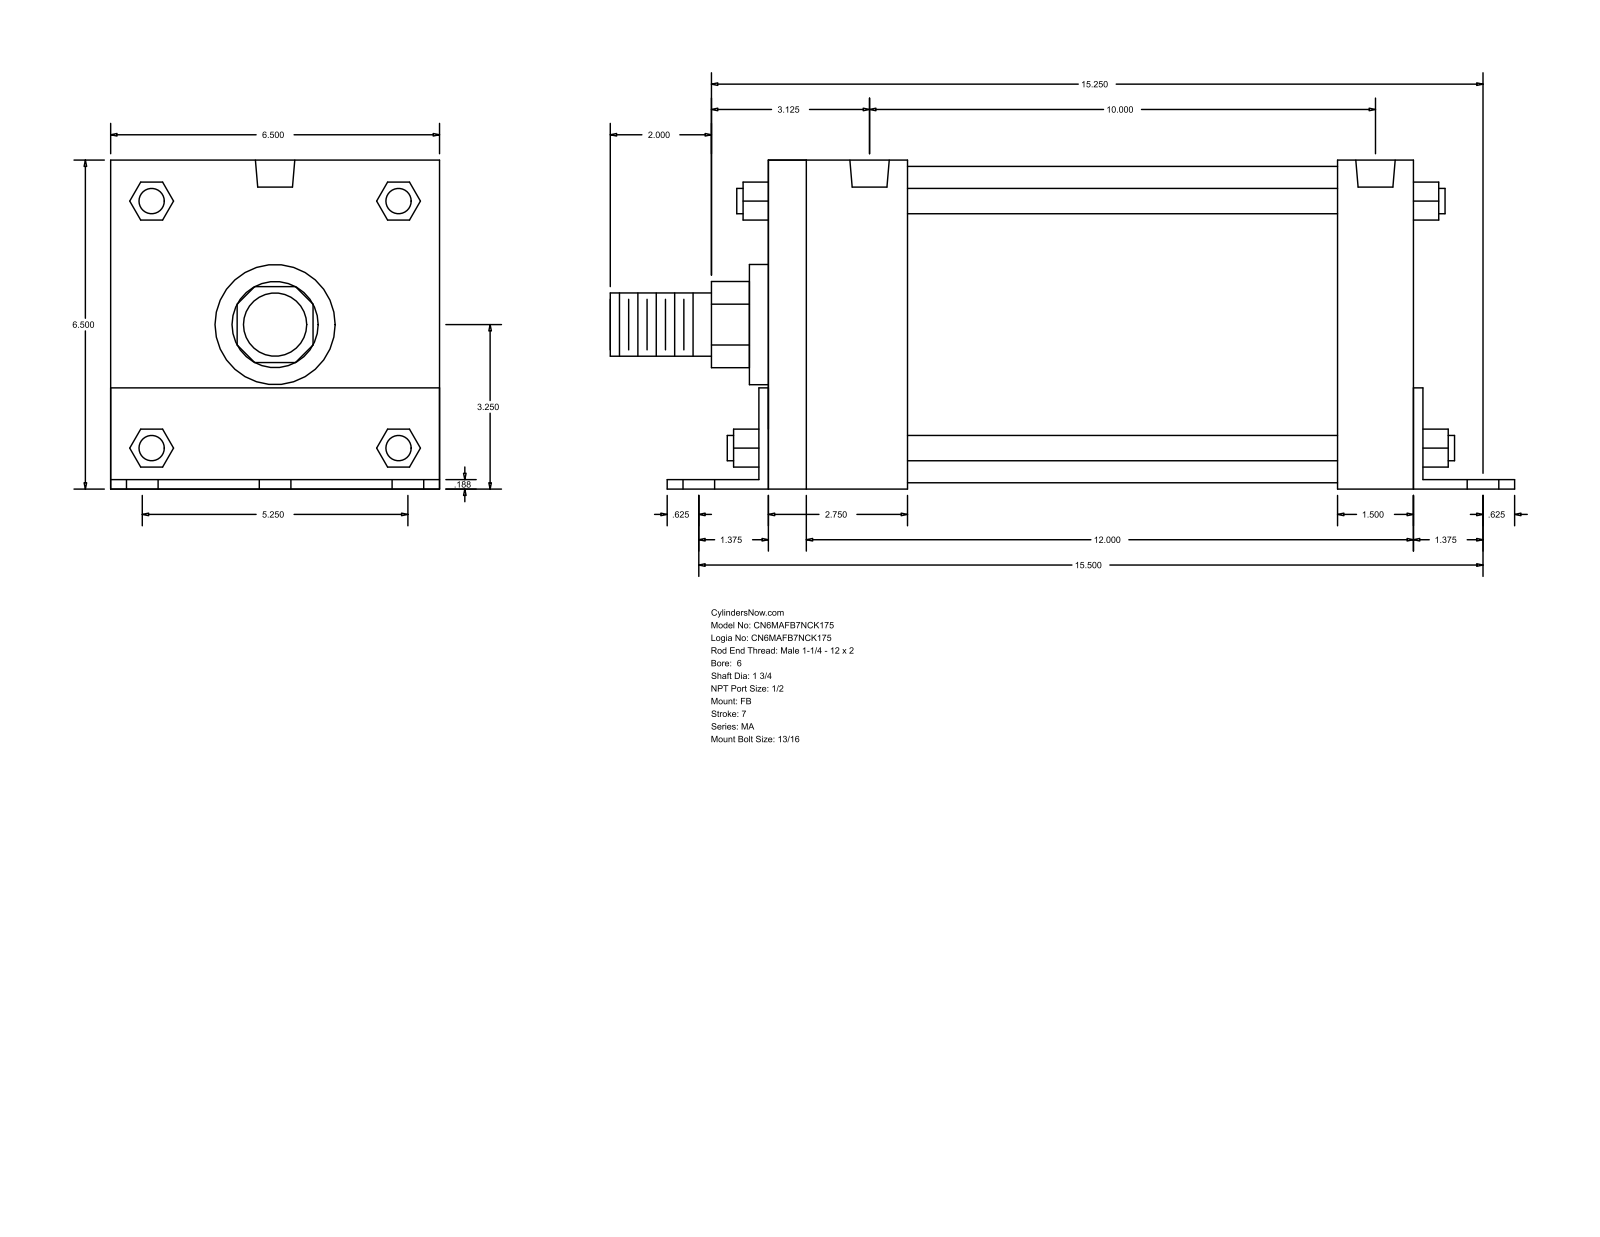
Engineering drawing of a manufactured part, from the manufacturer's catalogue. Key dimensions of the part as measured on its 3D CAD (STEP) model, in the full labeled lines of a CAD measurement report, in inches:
Part name (STEP PRODUCT): MA_FB__0600_1.75
STEP written by: GSSL Pune (CONFIG_CONTROL_DESIGN)
Units: inches
Bodies: 0 solids, 140 faces (105 planar, 35 cylindrical, 0 other)
Overall size (bounding box): 17.875 × 6.502 × 6.5
Round holes (diameter × count): ⌀0.813 ×6, ⌀0.687 ×4, ⌀0.778 ×2
Round bosses / shafts (diameter × count): ⌀0.5 ×4, ⌀6.25 ×1, ⌀2.375 ×1, ⌀1.75 ×1, ⌀1.25 ×1
Partial cylindrical surfaces — rounded edges, fillets, slot ends (radius × count): R0.852 ×1, R1.262 ×1
Main face-to-face distances: 6.5, 0.187, 12.75, 6.502, 12.938, 0.185, 6.315, 13.125, 1.5, 2.75
Hole centre spacings: 2.625, 15.721, 15.5, 3.377, 4.276, 5.25, 10, 12.406
